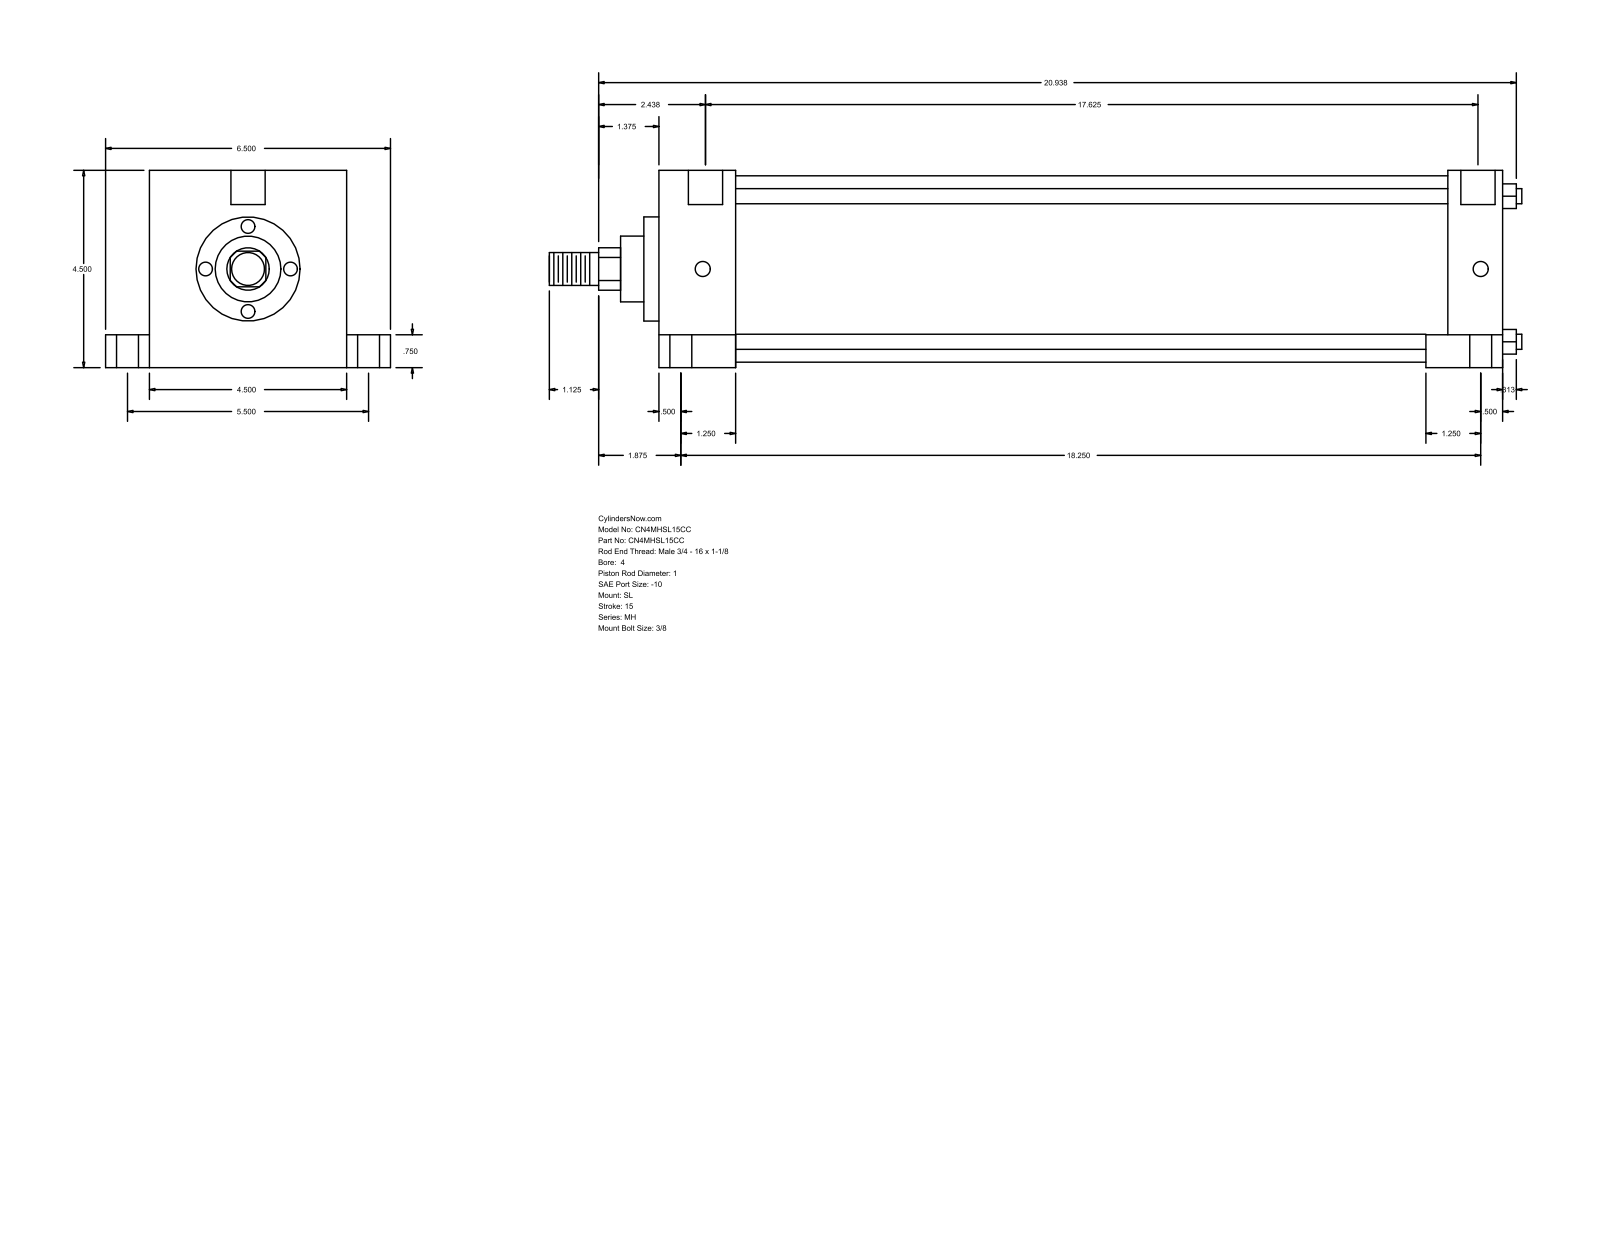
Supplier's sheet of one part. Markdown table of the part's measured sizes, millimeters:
| quantity | value |
| --- | --- |
| part name | MH_SL__0400_1 |
| STEP written by | GSSL Pune (CONFIG_CONTROL_DESIGN) |
| units | millimeters |
| bodies | 0 solids, 110 faces (77 planar, 33 cylindrical, 0 other) |
| overall size | 563.56 × 165.1 × 114.3 |
| round holes (diameter × count) | 8.73 × 4, 12.7 × 4, 19.05 × 4, 19.84 × 2 |
| round bosses / shafts (diameter × count) | 8.76 × 4, 107.95 × 1, 60.33 × 1, 38.1 × 1, 25.4 × 1, 19.05 × 1 |
| partial cylindrical surfaces (radius × count) | 12.29 × 1 |
| main face-to-face distances | 114.3, 488.96, 44.46, 444.5, 457.2, 412.74, 31.76, 25.4, 139.7, 19.05 |
| hole center spacings | 69.85, 69.87, 71, 71.3, 139.7, 450.85, 454.67, 456.23 |
